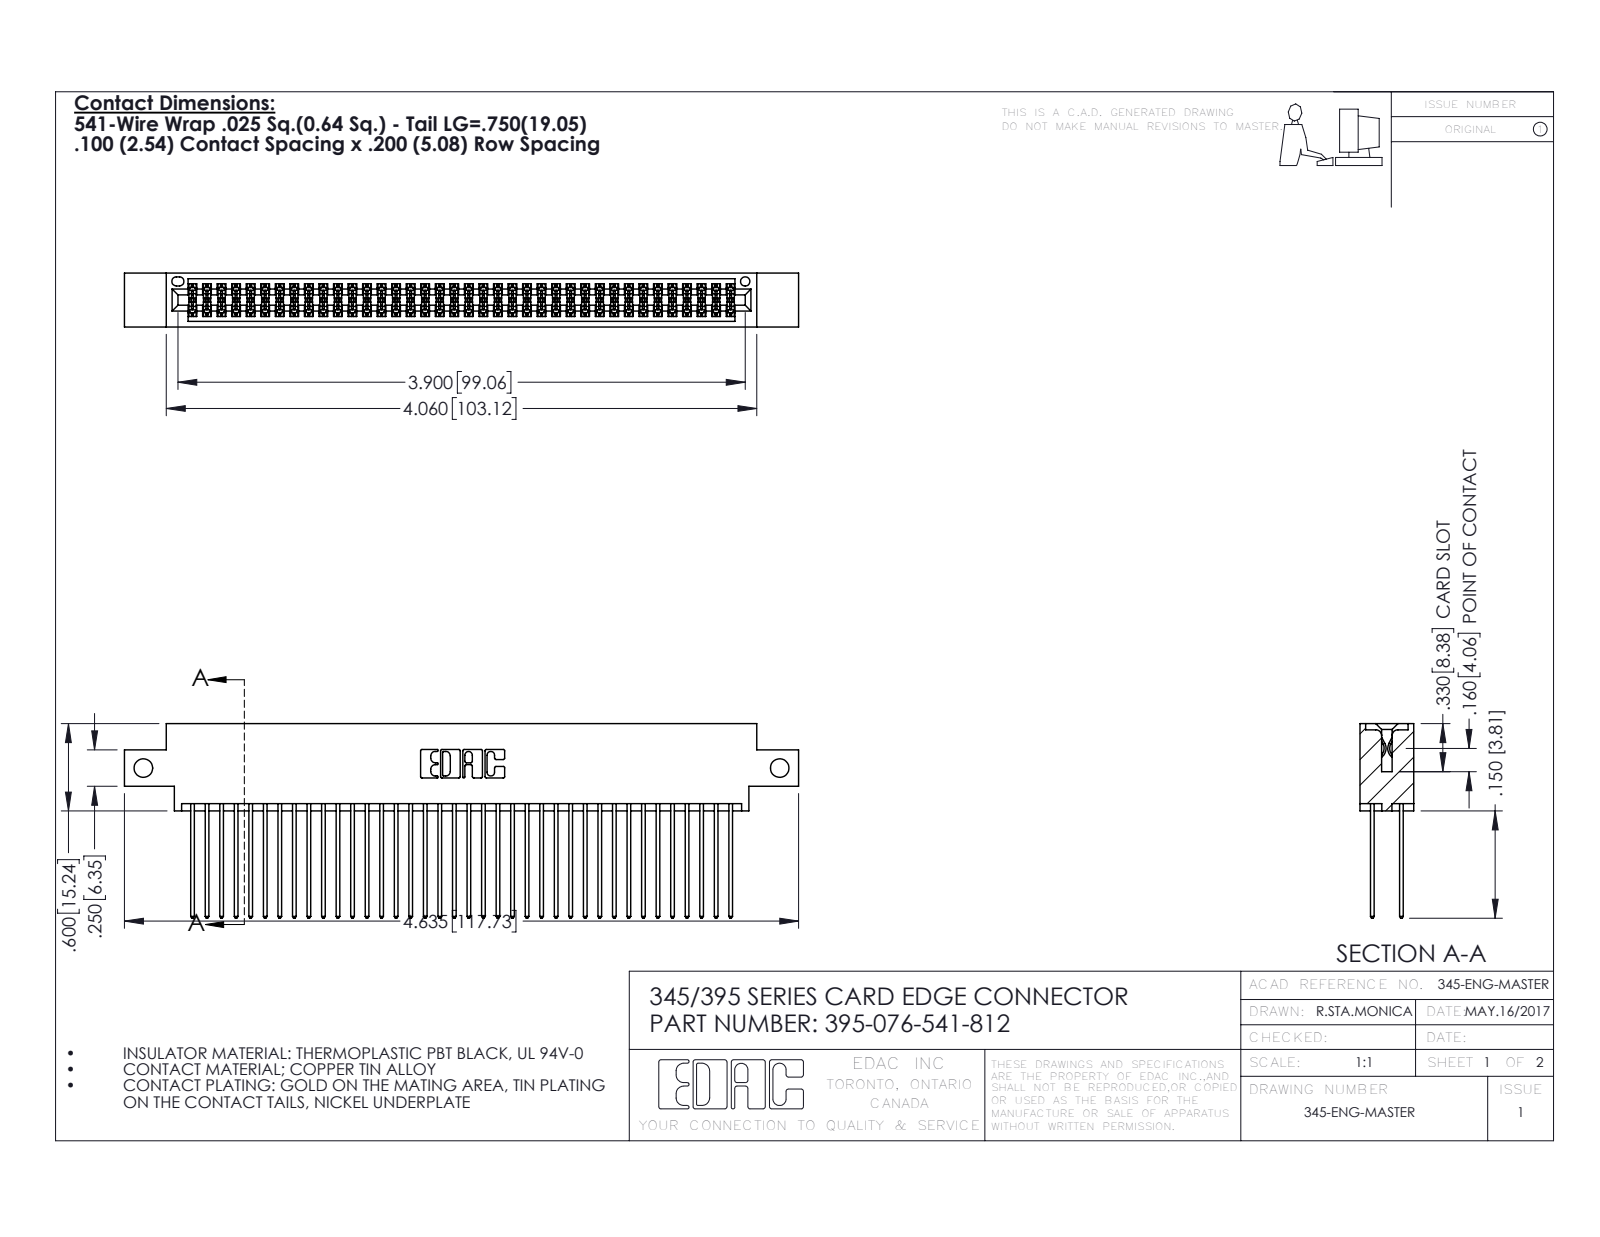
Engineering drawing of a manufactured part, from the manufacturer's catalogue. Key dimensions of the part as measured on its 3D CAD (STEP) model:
Part name (STEP PRODUCT): 395-076-541-812; 345 Part_0.170 Offset - Side Mount; 345-292-001_345-293-141
STEP written by: SolidWorks 2016 (CONFIG_CONTROL_DESIGN)
Units: inches
Bodies: 77 solids, 3930 faces (2592 planar, 1338 cylindrical, 0 other)
Overall size (bounding box): 4.635 × 1.337 × 0.37
Volume: 0.71 in³ · Surface area: 29.73 in²
Round holes (diameter × count): ⌀0.128 ×2, ⌀0.064 ×1
Partial cylindrical surfaces — rounded edges, fillets, slot ends (radius × count): R0.006 ×114, R0.01 ×76, R0.01 ×22, R0.007 ×6, R0.031 ×6, R0.026 ×3, R0.014 ×2, R0.019 ×2
Main face-to-face distances: 0.072, 0.298, 0.2, 0.098, 0.272, 0.025, 0.37, 0.225, 0.175, 0.149
Hole centre spacings: 4.375
